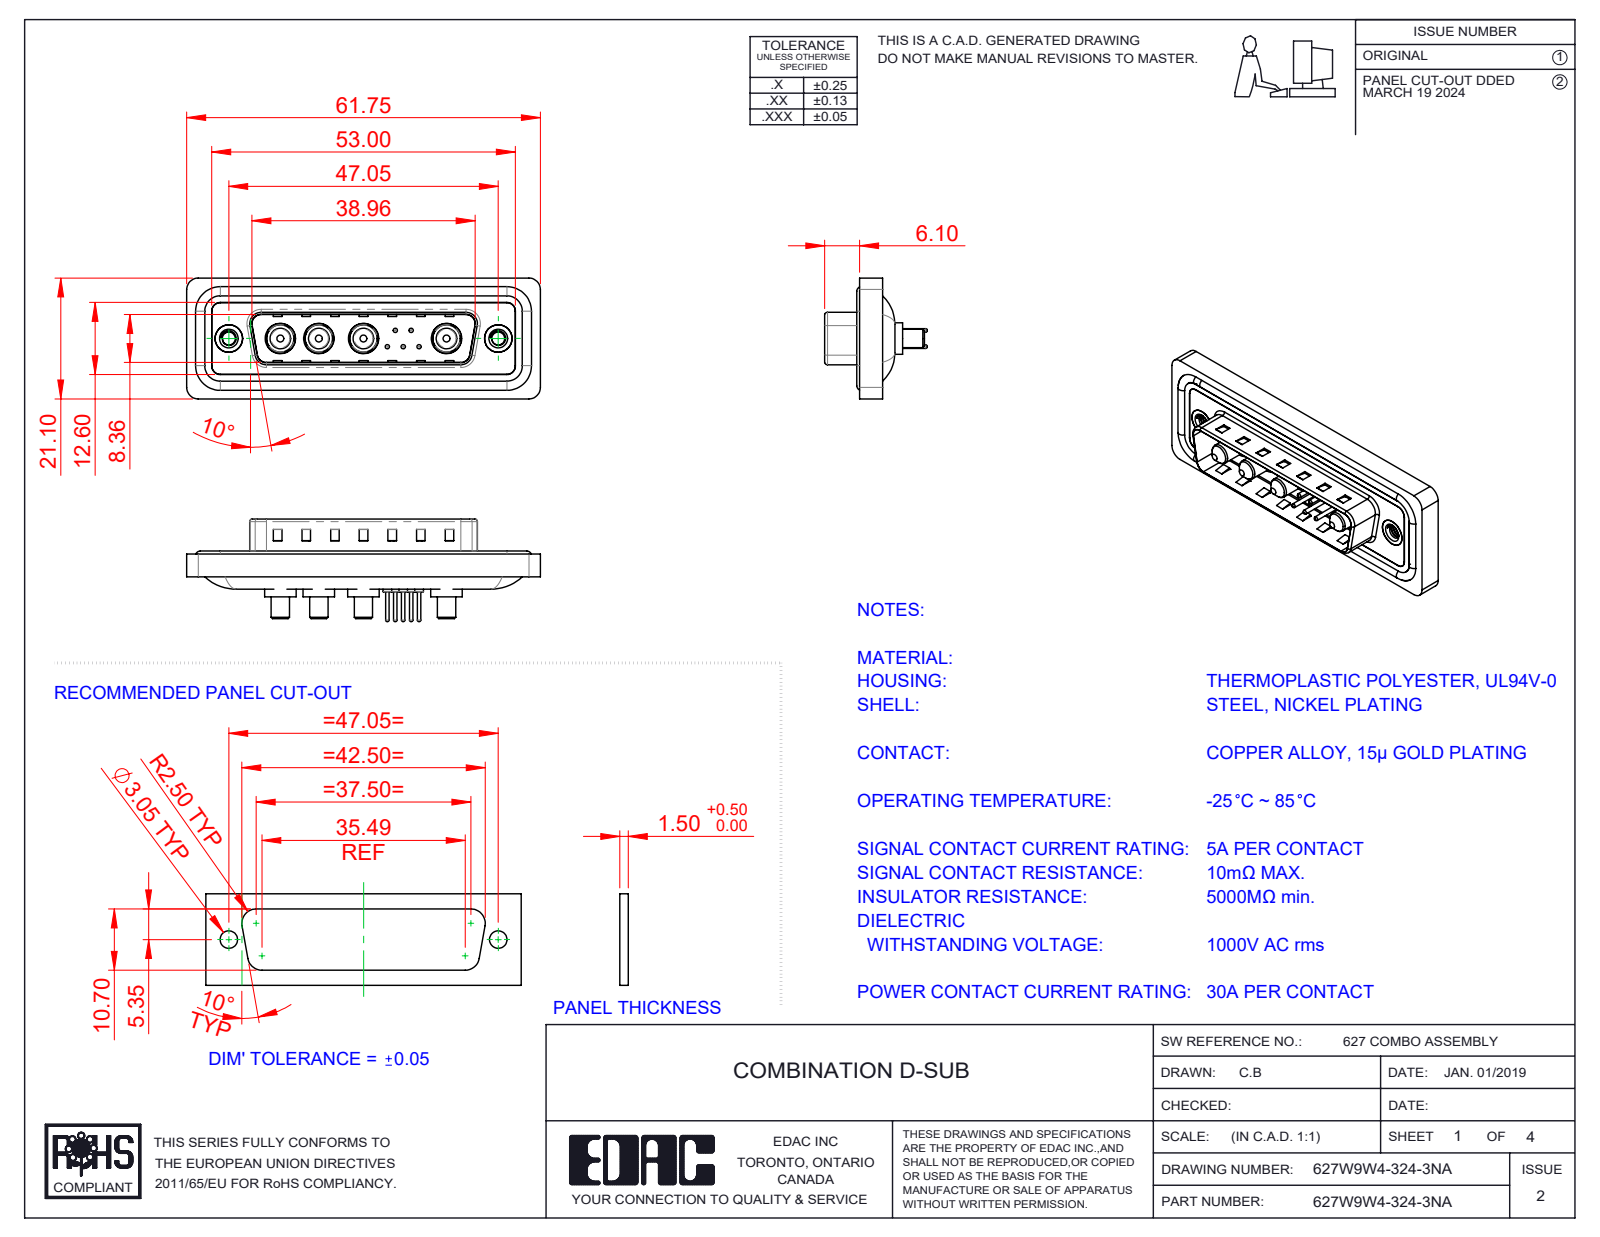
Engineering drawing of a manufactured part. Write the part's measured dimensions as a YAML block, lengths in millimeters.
part_name: "627Combo Contact Row 2_24; 627Combo Shell Rear_25 Contacts; 627Combo Waterproof Housing_25 Contacts; 627Combo Contact Row 1_24 (+5 more)"
step_written_by: "SolidWorks 2023 (CONFIG_CONTROL_DESIGN)"
units: millimeters
bodies: {solids: 20, faces: 822, planar: 284, cylindrical: 336, other: 202}
overall_size: [61.75, 21.1, 17.9]
volume: 7434
surface_area: 11851
round_holes:
  - {diameter: 0.75, count: 5}
  - {diameter: 1.6, count: 5}
  - {diameter: 2, count: 5}
  - {diameter: 4.85, count: 4}
  - {diameter: 5.3, count: 4}
  - {diameter: 2.26, count: 2}
  - {diameter: 4, count: 2}
  - {diameter: 4.8, count: 2}
  - {diameter: 5, count: 2}
round_bosses_or_shafts:
  - {diameter: 1.5, count: 5}
  - {diameter: 0.6, count: 5}
  - {diameter: 5.5, count: 4}
  - {diameter: 5.2, count: 4}
  - {diameter: 4.75, count: 4}
  - {diameter: 3.75, count: 4}
  - {diameter: 3.6, count: 4}
  - {diameter: 3.2, count: 4}
partial_cylinders:
  - {radius: 1.5, count: 22}
  - {radius: 2, count: 18}
  - {radius: 0.5, count: 8}
  - {radius: 1.6, count: 8}
  - {radius: 0.25, count: 4}
  - {radius: 0.6, count: 4}
  - {radius: 0.65, count: 4}
  - {radius: 0.9, count: 4}
face_to_face_distances: [0.4, 1.5, 1.1, 0.5, 1.6, 3.1, 2.9, 0.82, 9.58, 5.65]
hole_center_spacings: [3.16, 2.77, 5.04, 14.51, 2.78, 4.4, 4.41, 5]
